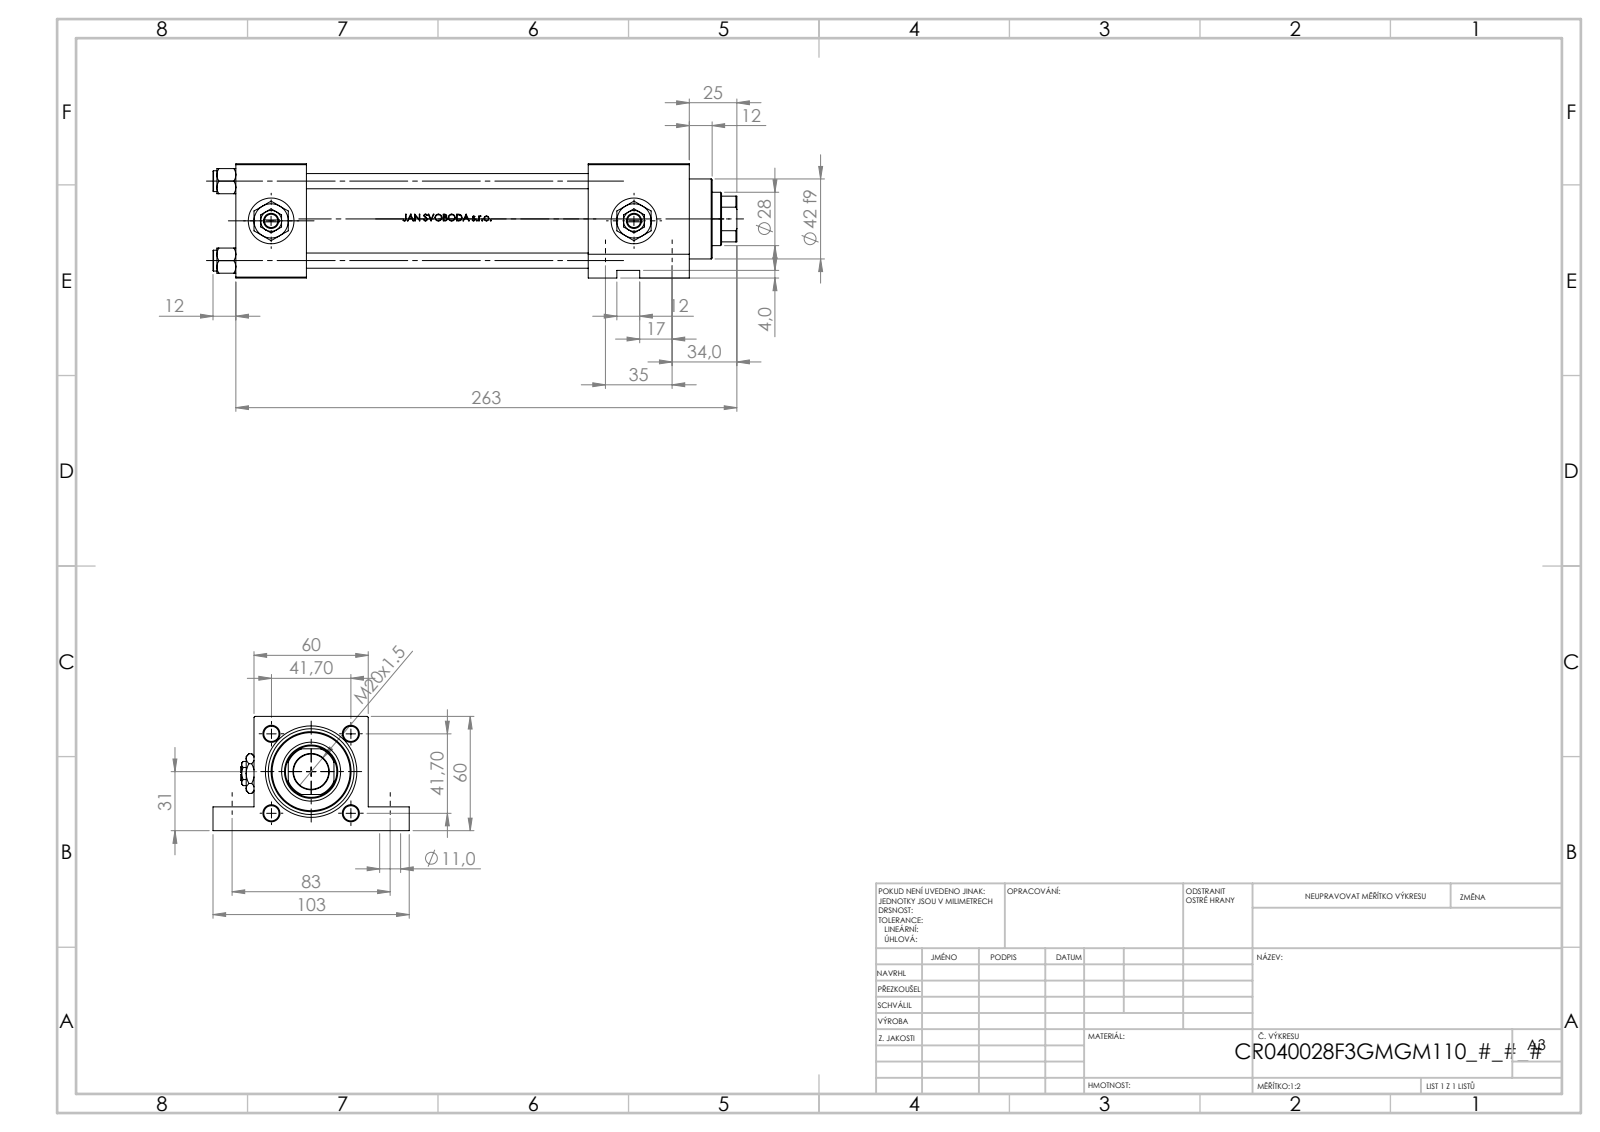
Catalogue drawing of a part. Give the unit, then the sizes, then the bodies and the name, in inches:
Units: inches
Overall size (bounding box): 10.827 × 4.055 × 2.362
Round holes (diameter × count): ⌀0.315 ×4, ⌀0.433 ×4, ⌀0.656 ×3, ⌀0.945 ×3, ⌀0.098 ×2, ⌀0.276 ×2, ⌀0.63 ×1, ⌀0.728 ×1, ⌀1.102 ×1, ⌀1.22 ×1, ⌀1.575 ×1, ⌀1.772 ×1
Round bosses / shafts (diameter × count): ⌀0.433 ×4, ⌀1.811 ×1, ⌀1.654 ×1
Partial cylindrical surfaces — rounded edges, fillets, slot ends (radius × count): R0.531 ×1
Main face-to-face distances: 2.362, 1.457, 7.283, 5.827, 9.37, 7.913, 2.087, 1.496, 1.87, 0.492
Hole centre spacings: 0.821, 1.161, 1.642, 1.832, 0.817, 1.378, 2.322, 3.268
Volume: 33.67 in³ · Surface area: 251 in²
Bodies: 13 solids, 1216 faces (486 planar, 148 cylindrical, 582 other)
Part name (STEP PRODUCT): V215CR_F_TYCINKA; V215_VC_A; V215CR_VCP_F; V215CR_F_Body (+2 more)
STEP written by: SolidWorks 2019 (CONFIG_CONTROL_DESIGN)
